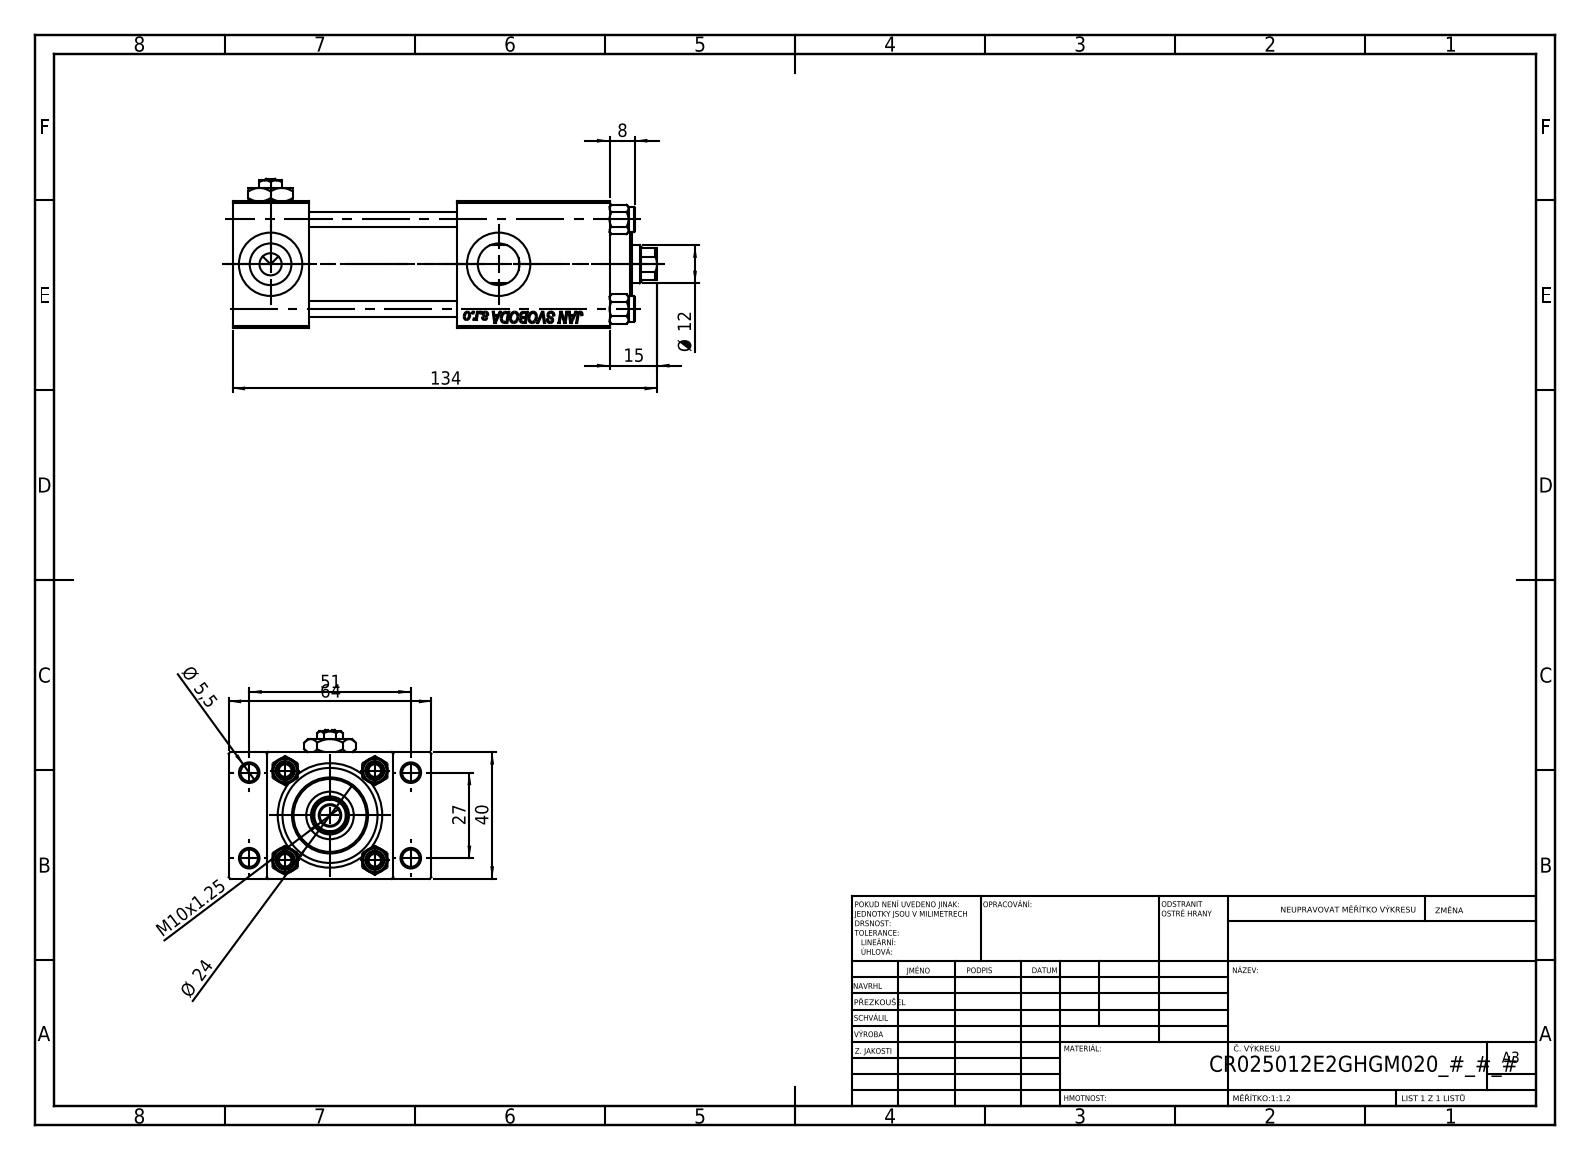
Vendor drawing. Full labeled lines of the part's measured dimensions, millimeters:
Part name (STEP PRODUCT): NUT_M5_E; Zatka_pro_OIL_PORT; V215CR_TYCINKA_E; V215CR_E_Body (+2 more)
STEP written by: SolidWorks 2019 (CONFIG_CONTROL_DESIGN)
Units: millimetres
Bodies: 12 solids, 1187 faces (520 planar, 93 cylindrical, 574 other)
Overall size (bounding box): 134 × 64 × 47
Volume: 162 456 mm³ · Surface area: 63 452 mm²
Round holes (diameter × count): ⌀5 ×4, ⌀5.5 ×4, ⌀20 ×4, ⌀7 ×3, ⌀13.16 ×3, ⌀6.5 ×1, ⌀12 ×1, ⌀15 ×1, ⌀25 ×1, ⌀30 ×1
Round bosses / shafts (diameter × count): ⌀8 ×4, ⌀31 ×1, ⌀24 ×1
Partial cylindrical surfaces — rounded edges, fillets, slot ends (radius × count): R5.5 ×1
Main face-to-face distances: 40, 24, 12, 52, 119, 95, 90.3, 66.3, 28.7, 47
Hole centre spacings: 11.37, 20.01, 28.3, 28.85, 29.89, 39.66, 48.34, 27
